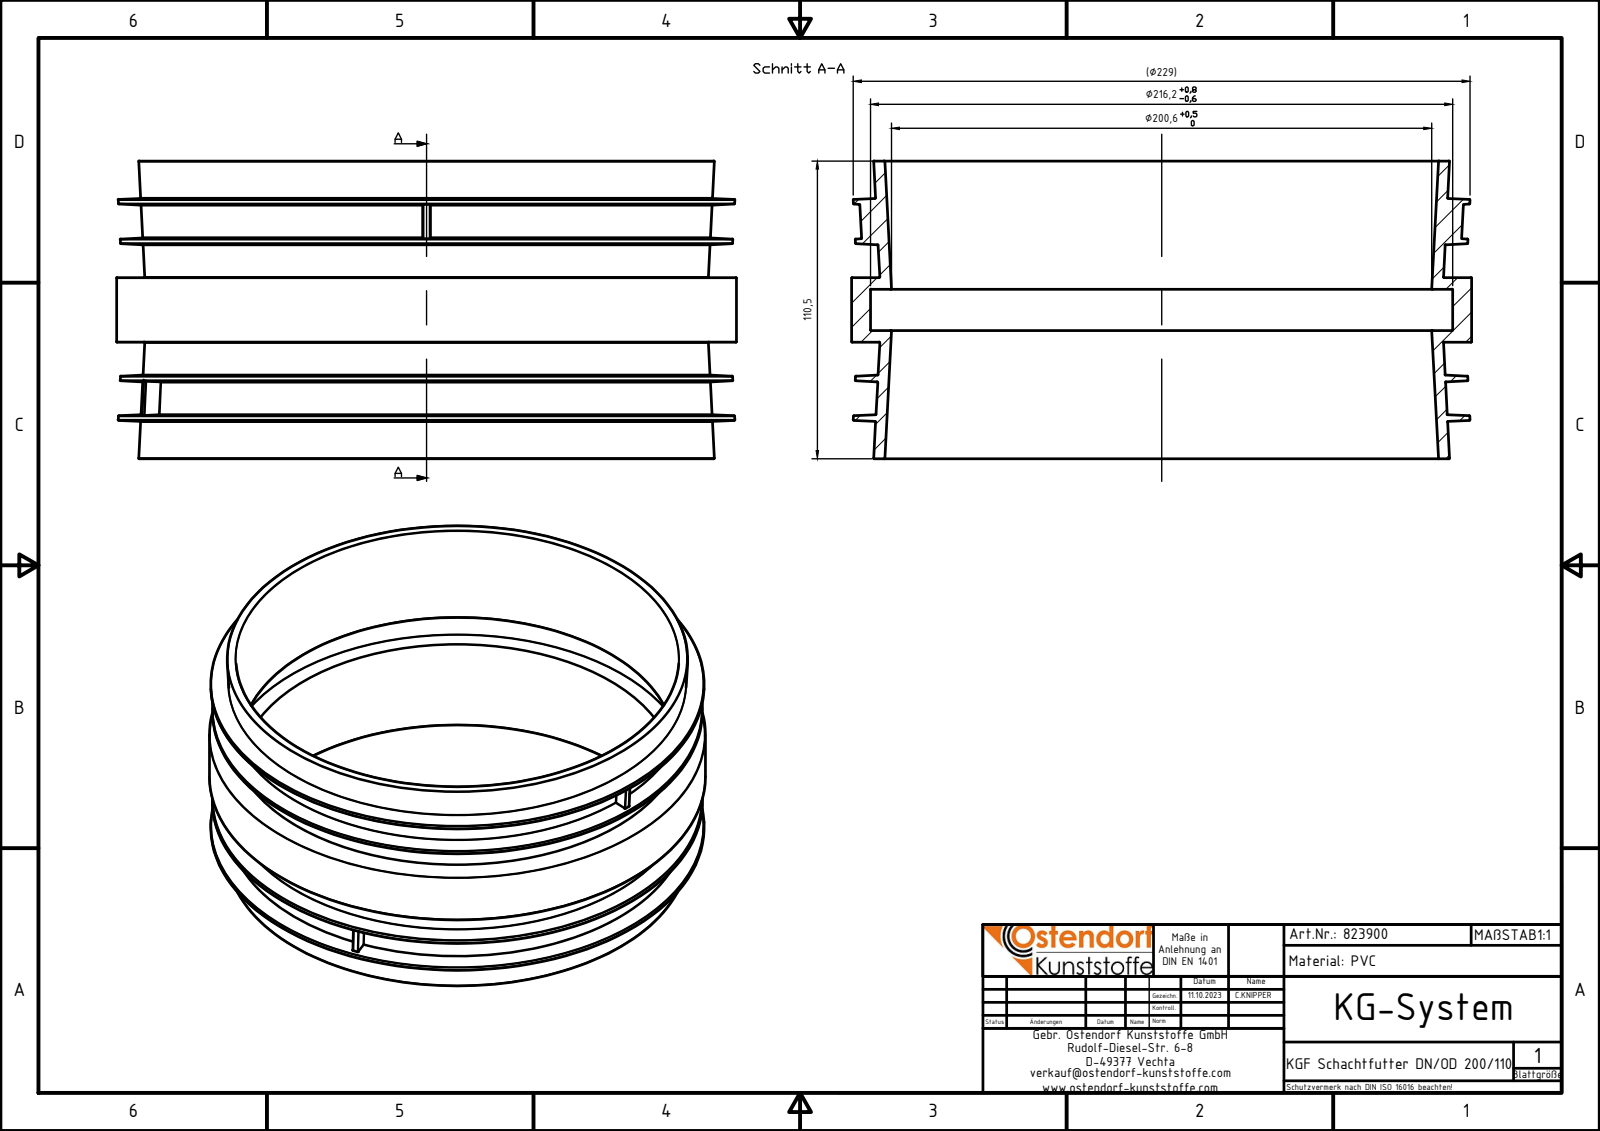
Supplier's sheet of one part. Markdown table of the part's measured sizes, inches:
| quantity | value |
| --- | --- |
| part name | 823900z |
| STEP written by | Autodesk Inventor 2024 (AUTOMOTIVE_DESIGN) |
| units | inches |
| bodies | 1 solid, 138 faces (18 planar, 10 cylindrical, 110 other) |
| overall size | 9.063 × 9.063 × 4.35 |
| volume | 26.99 in³ |
| surface area | 340.1 in² |
| round holes (diameter × count) | 8.512 × 1 |
| round bosses / shafts (diameter × count) | 9.063 × 1 |
| partial cylindrical surfaces (radius × count) | 0.008 × 8 |
| main face-to-face distances | 0.171, 0.774, 0.945, 1.703, 1.874, 2.476, 2.648, 0.602, 4.35, 0.106 |
